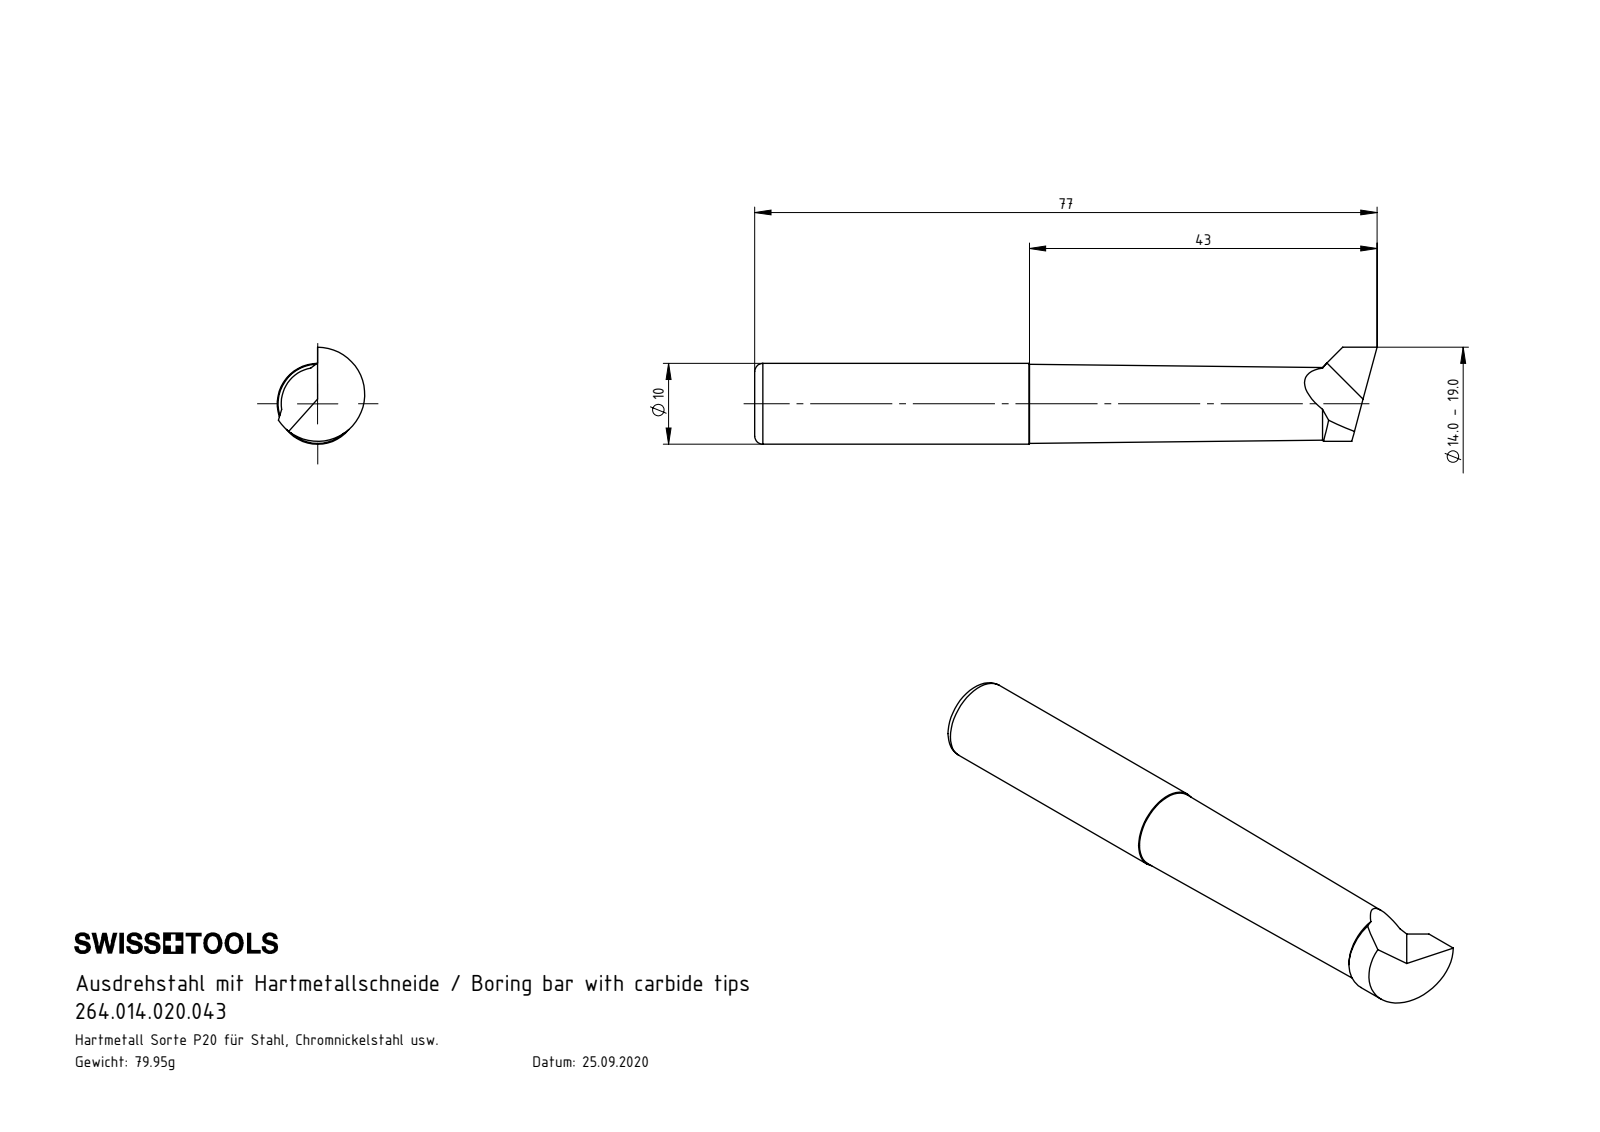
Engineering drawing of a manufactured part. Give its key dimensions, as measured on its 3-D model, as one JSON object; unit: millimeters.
{"part_name": "U10.B14.002.043", "step_written_by": "SolidWorks 2017 (AUTOMOTIVE_DESIGN)", "units": "millimeters", "bodies": {"solids": 1, "faces": 10, "planar": 4, "cylindrical": 2, "other": 4}, "overall_size": [77, 12, 10.82], "volume_mm3": 5514, "surface_area_mm2": 2452, "round_bosses_or_shafts": [[10, 1]], "partial_cylinders_radius": [[5.82, 1]]}
